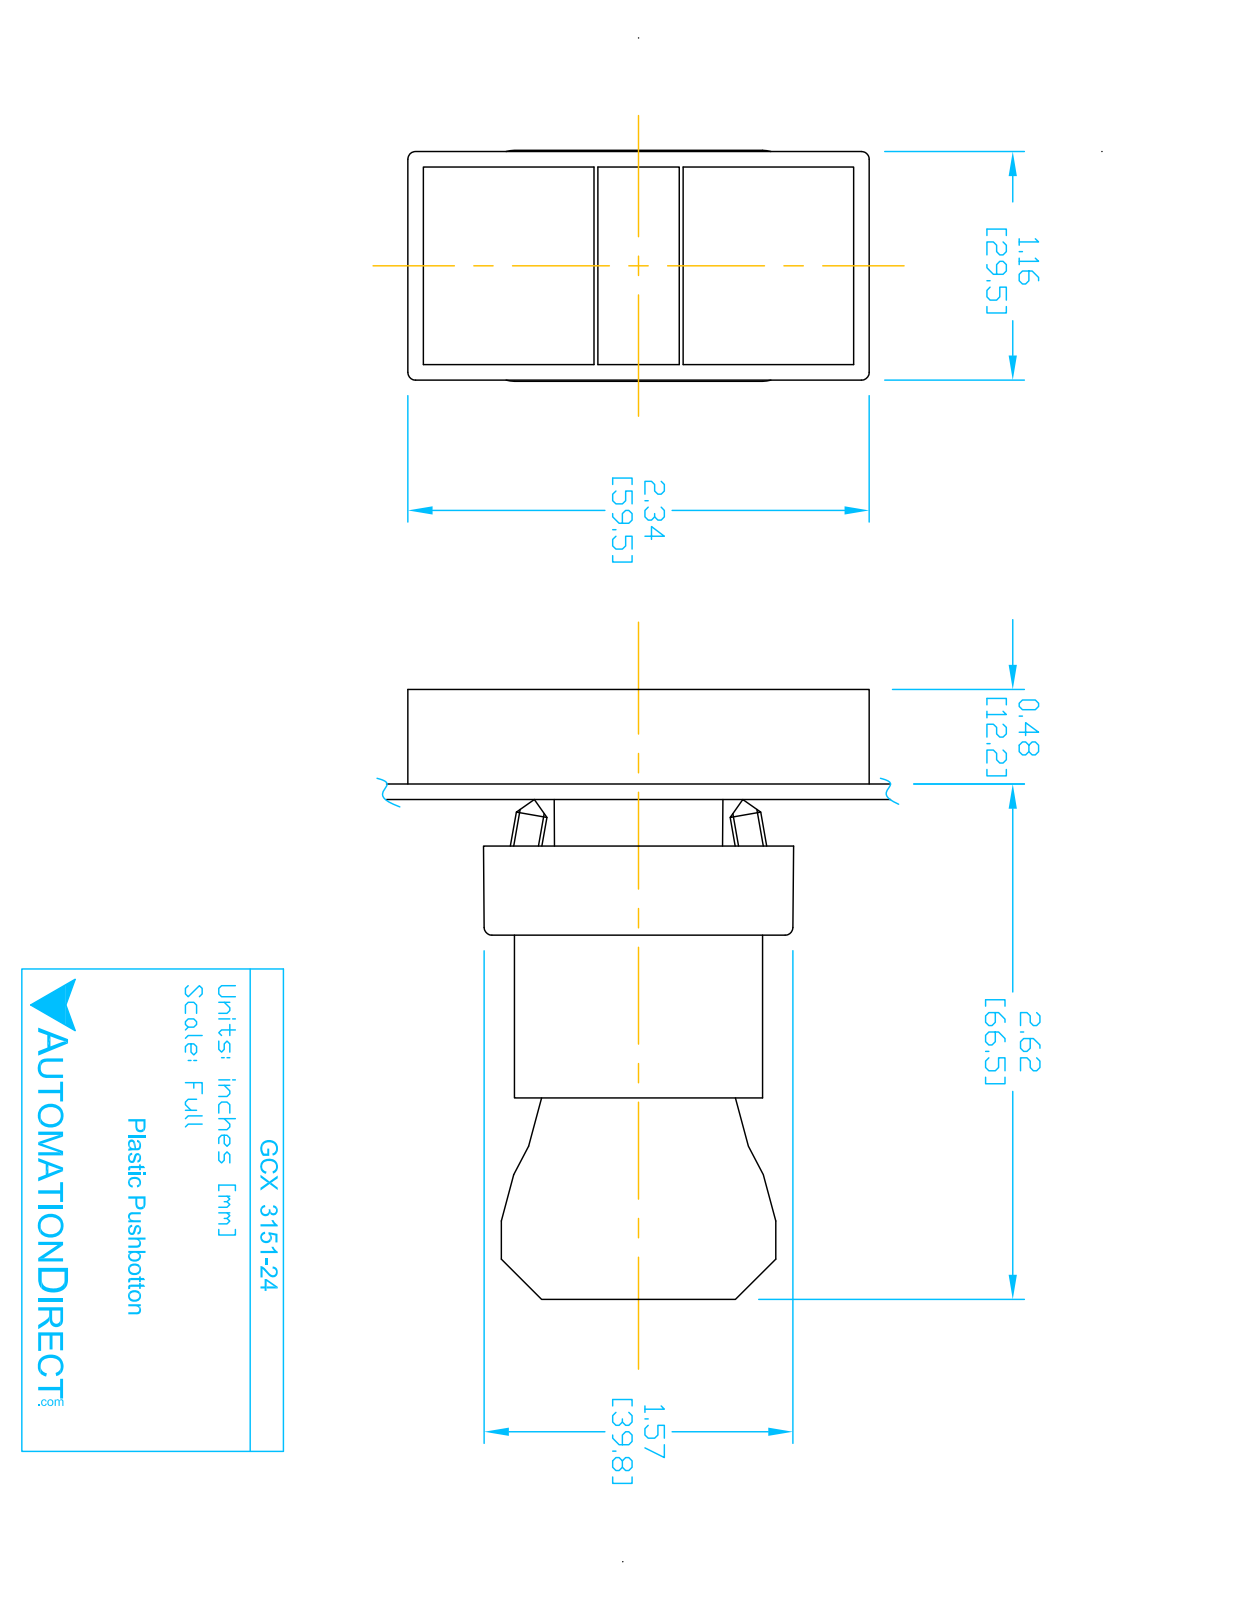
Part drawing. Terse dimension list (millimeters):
name: GCX3151-24; ECX1050; GCX3151-24 OPERATOR; ECX3029-2 (+2 more)
written by: SolidWorks 2016 (AUTOMOTIVE_DESIGN)
unit: mm
bodies: 9 solids, 531 faces (348 planar, 152 cylindrical, 31 other)
size: 77.3 × 59.5 × 29.9
volume: 70 150 mm³; area: 35 980 mm²
holes: 4× ⌀2, 2× ⌀2.2, 2× ⌀3.1, 2× ⌀3.3, 1× ⌀5, 1× ⌀11.9, 1× ⌀22.3, 1× ⌀22.6
bosses: 4× ⌀4, 1× ⌀24, 1× ⌀21.7, 1× ⌀19.8, 1× ⌀12.8
rounds: 24× R1.5, 12× R1, 12× R3.1, 12× R4, 8× R1, 2× R1.6, 2× R2, 2× R3.3
face distances: 1, 1.5, 0.5, 11.5, 14.7, 15.1, 18.8, 30.3, 21, 39.8
hole spacings: 6, 25.5, 24.7, 12, 13.7, 13.8, 27.5, 12.3
